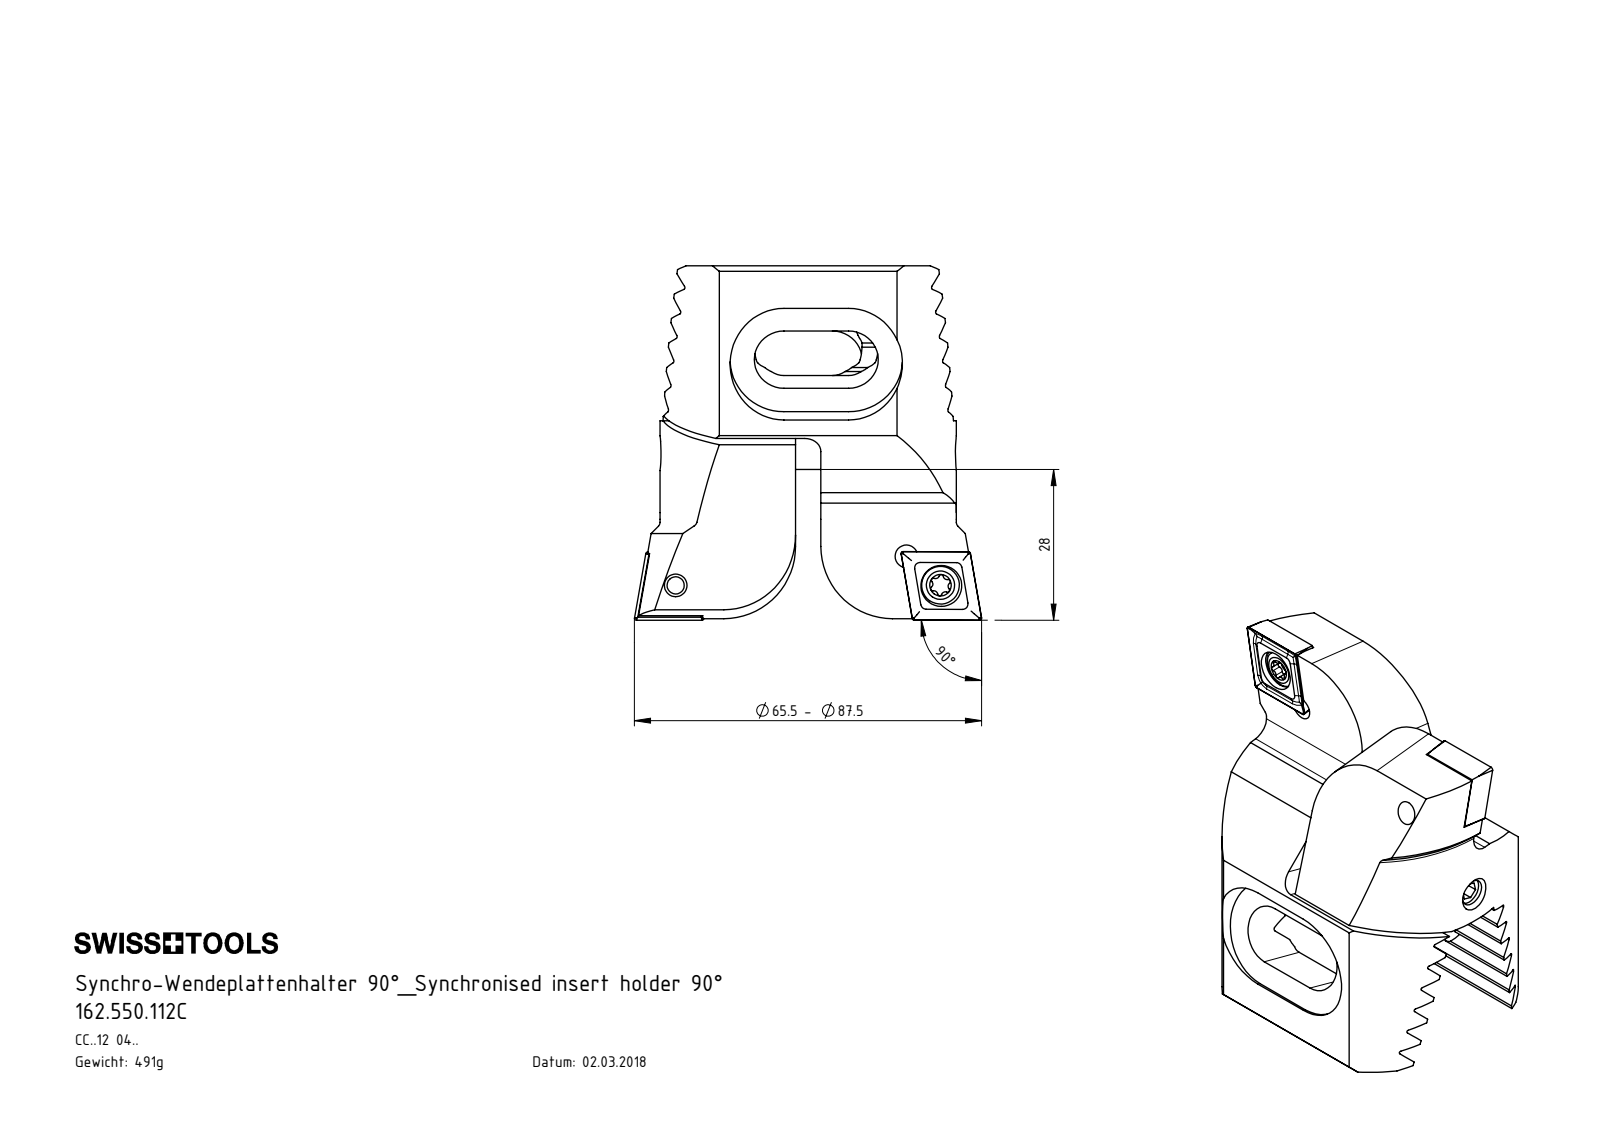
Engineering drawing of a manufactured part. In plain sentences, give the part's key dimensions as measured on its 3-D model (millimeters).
The part is named "Z55-WCC.003.037_A; Z42-ER3.002.005_A; Z55-WCC.001.037_A; Z55-ER3.001.052_A (+4 more)". Its 3-D file was written by "SolidWorks 2017 (CONFIG_CONTROL_DESIGN)". It is 11 solids with 484 faces: 187 planar, 155 cylindrical and 142 other. Overall it measures 65.75 by 64.42 by 44 millimeters. Its volume is 62 568 cubic millimeters and its surface area 24 121 square millimeters. Round holes: 4 of diameter 4.2, 3 of diameter 1, 3 of diameter 3.3, 2 of diameter 5.5, 2 of diameter 7.6, 1 of diameter 5. Round bosses or shafts: 3 of diameter 4, 2 of diameter 7, 2 of diameter 5, 1 of diameter 17, 1 of diameter 6, 1 of diameter 3.8. Partial cylindrical surfaces (rounded edges, fillets, slot ends): 12 of radius 0.34, 12 of radius 0.39, 12 of radius 0.69, 8 of radius 1, 4 of radius 3, 4 of radius 5.5, 4 of radius 10, 2 of radius 13.3. The main face-to-face distances are 4.07, 8.14, 12.21, 16.28, 20.35, 4.85, 17.24, 1, 7.12, 21.7. The hole center spacings are 8.29, 3, 8.49, 8.5, 14.99, 15, 15.3, 28.36.
